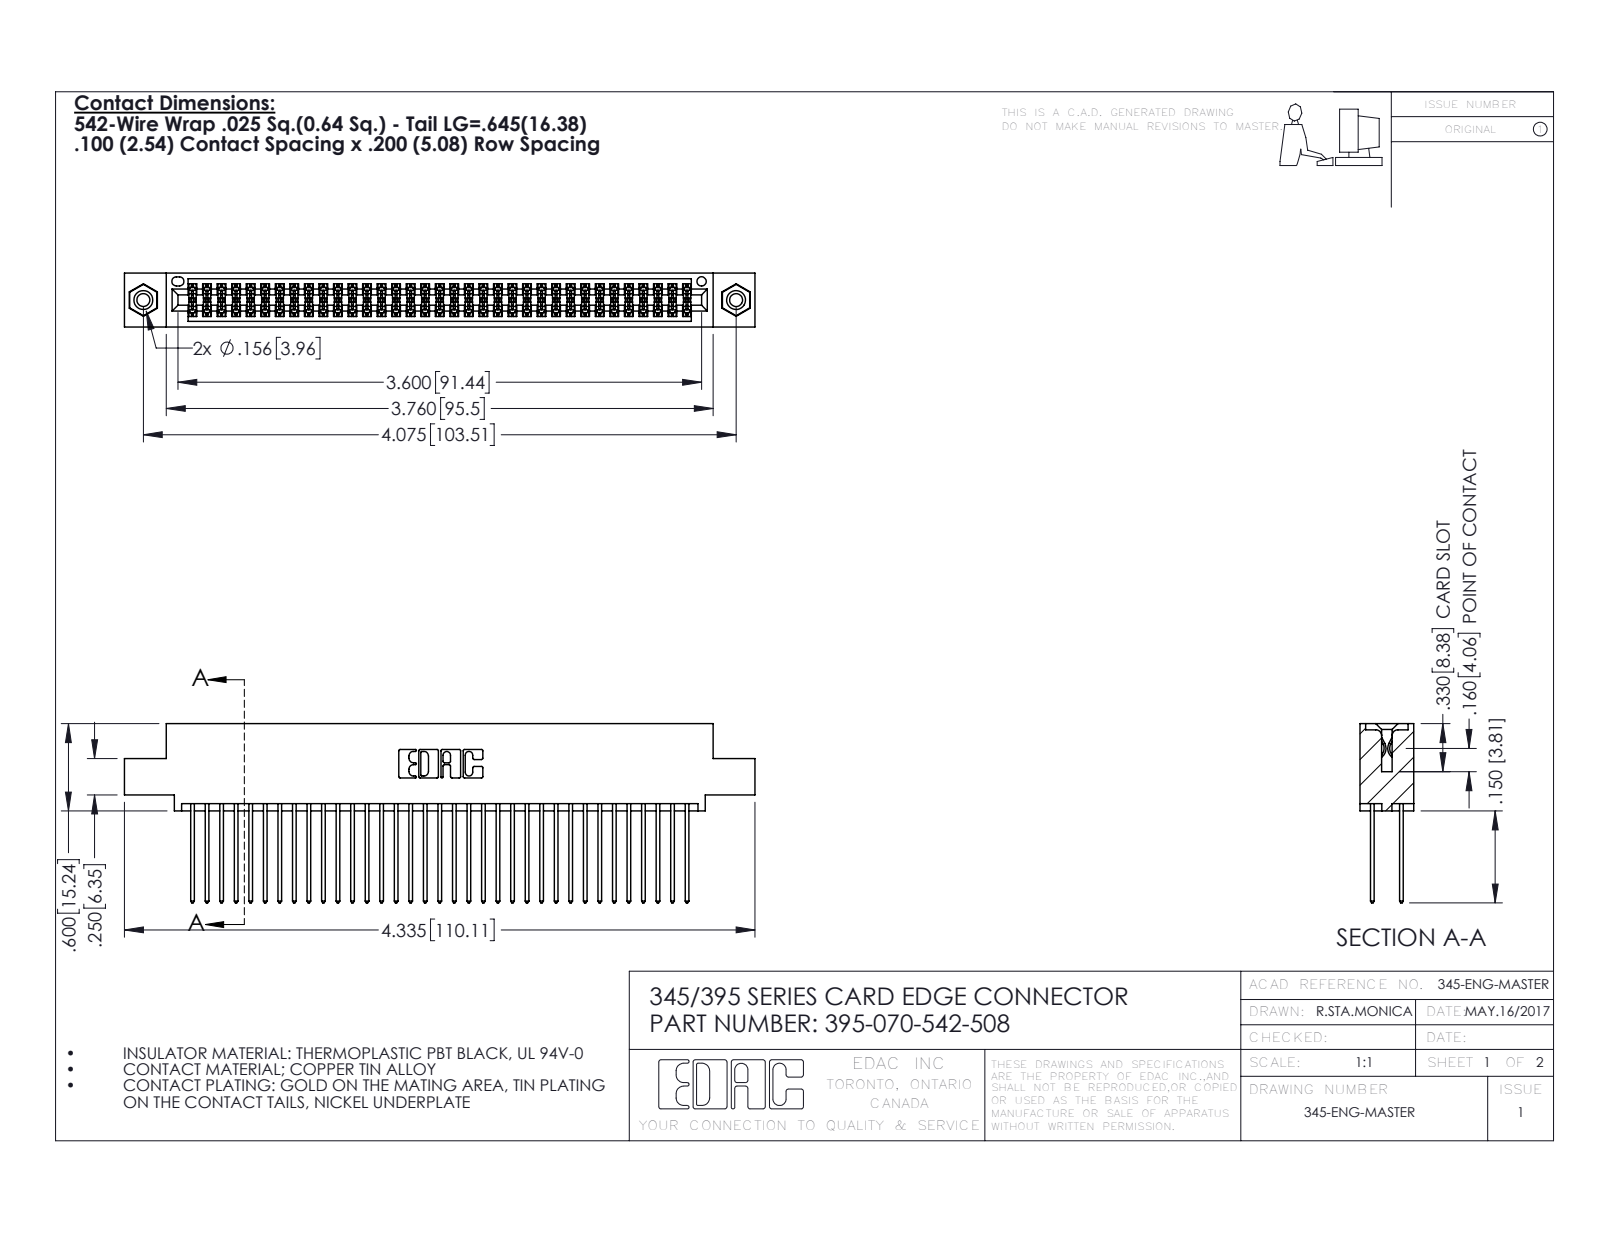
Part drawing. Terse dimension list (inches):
name: 345-250-001_345-250-003-102; 395-070-542-508; 345 Part_0.110 Offset - 0.156 Dia-TI; 345-292-001_345-293-142
written by: SolidWorks 2016 (CONFIG_CONTROL_DESIGN)
unit: in
bodies: 73 solids, 3690 faces (2426 planar, 1248 cylindrical, 16 other)
size: 4.335 × 1.232 × 0.37
volume: 0.664 in³; area: 27.24 in²
holes: 2× ⌀0.089, 2× ⌀0.125, 2× ⌀0.156, 1× ⌀0.064
bosses: 2× ⌀0.155
rounds: 105× R0.006, 70× R0.01, 22× R0.01, 6× R0.007, 6× R0.031, 3× R0.026, 2× R0.014, 2× R0.019
face distances: 0.072, 0.298, 0.2, 0.098, 0.272, 0.025, 0.37, 0.225, 0.175, 0.149
hole spacings: 0.27, 3.839, 4.075
